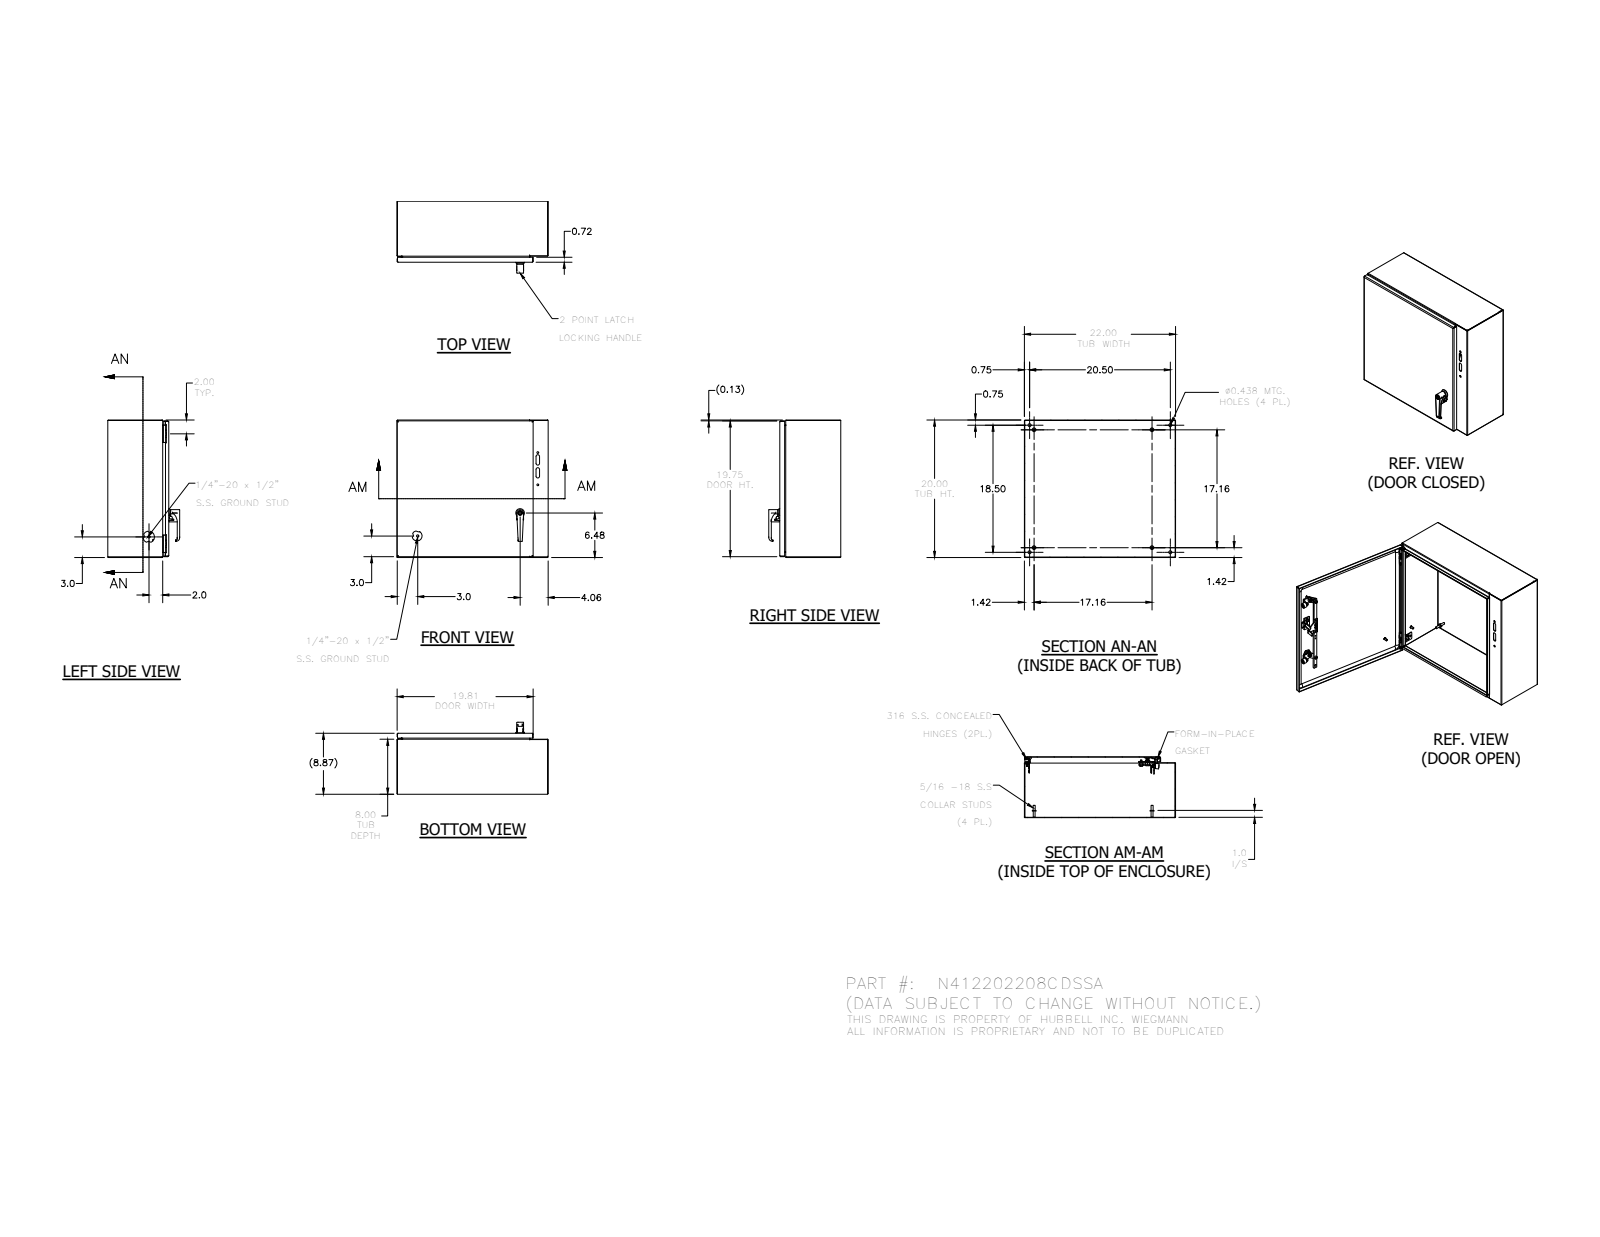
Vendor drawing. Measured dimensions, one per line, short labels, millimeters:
name: N412202208CDSSA
written by: SolidWorks 2019 (AUTOMOTIVE_DESIGN)
unit: mm
bodies: 61 solids, 2081 faces (813 planar, 739 cylindrical, 529 other)
size: 558.8 × 508 × 265.8
volume: 1 963 000 mm³; area: 2 361 000 mm²
holes: 4× ⌀2.4, 4× ⌀3.7, 4× ⌀3.9, 4× ⌀4, 4× ⌀4.2, 4× ⌀4.4, 4× ⌀4.7, 4× ⌀11.1, 3× ⌀8.1, 2× ⌀5, 2× ⌀5.4, 2× ⌀5.6
bosses: 12× ⌀6.4, 8× ⌀7.6, 4× ⌀14.3, 4× ⌀11.1, 4× ⌀9.1, 4× ⌀8.1, 4× ⌀6.5, 4× ⌀5.7
rounds: 38× R0.5, 31× R0.3, 26× R1.3, 25× R3.2, 18× R0.4, 16× R0.6, 16× R0.8, 16× R2.3
face distances: 1.5, 223.8, 222.3, 225.3, 506.5, 508, 505, 201.7, 22.1, 1.5
hole spacings: 406.4, 16.8, 12.7, 16.7, 49.9, 269.9, 423.2, 446.6
